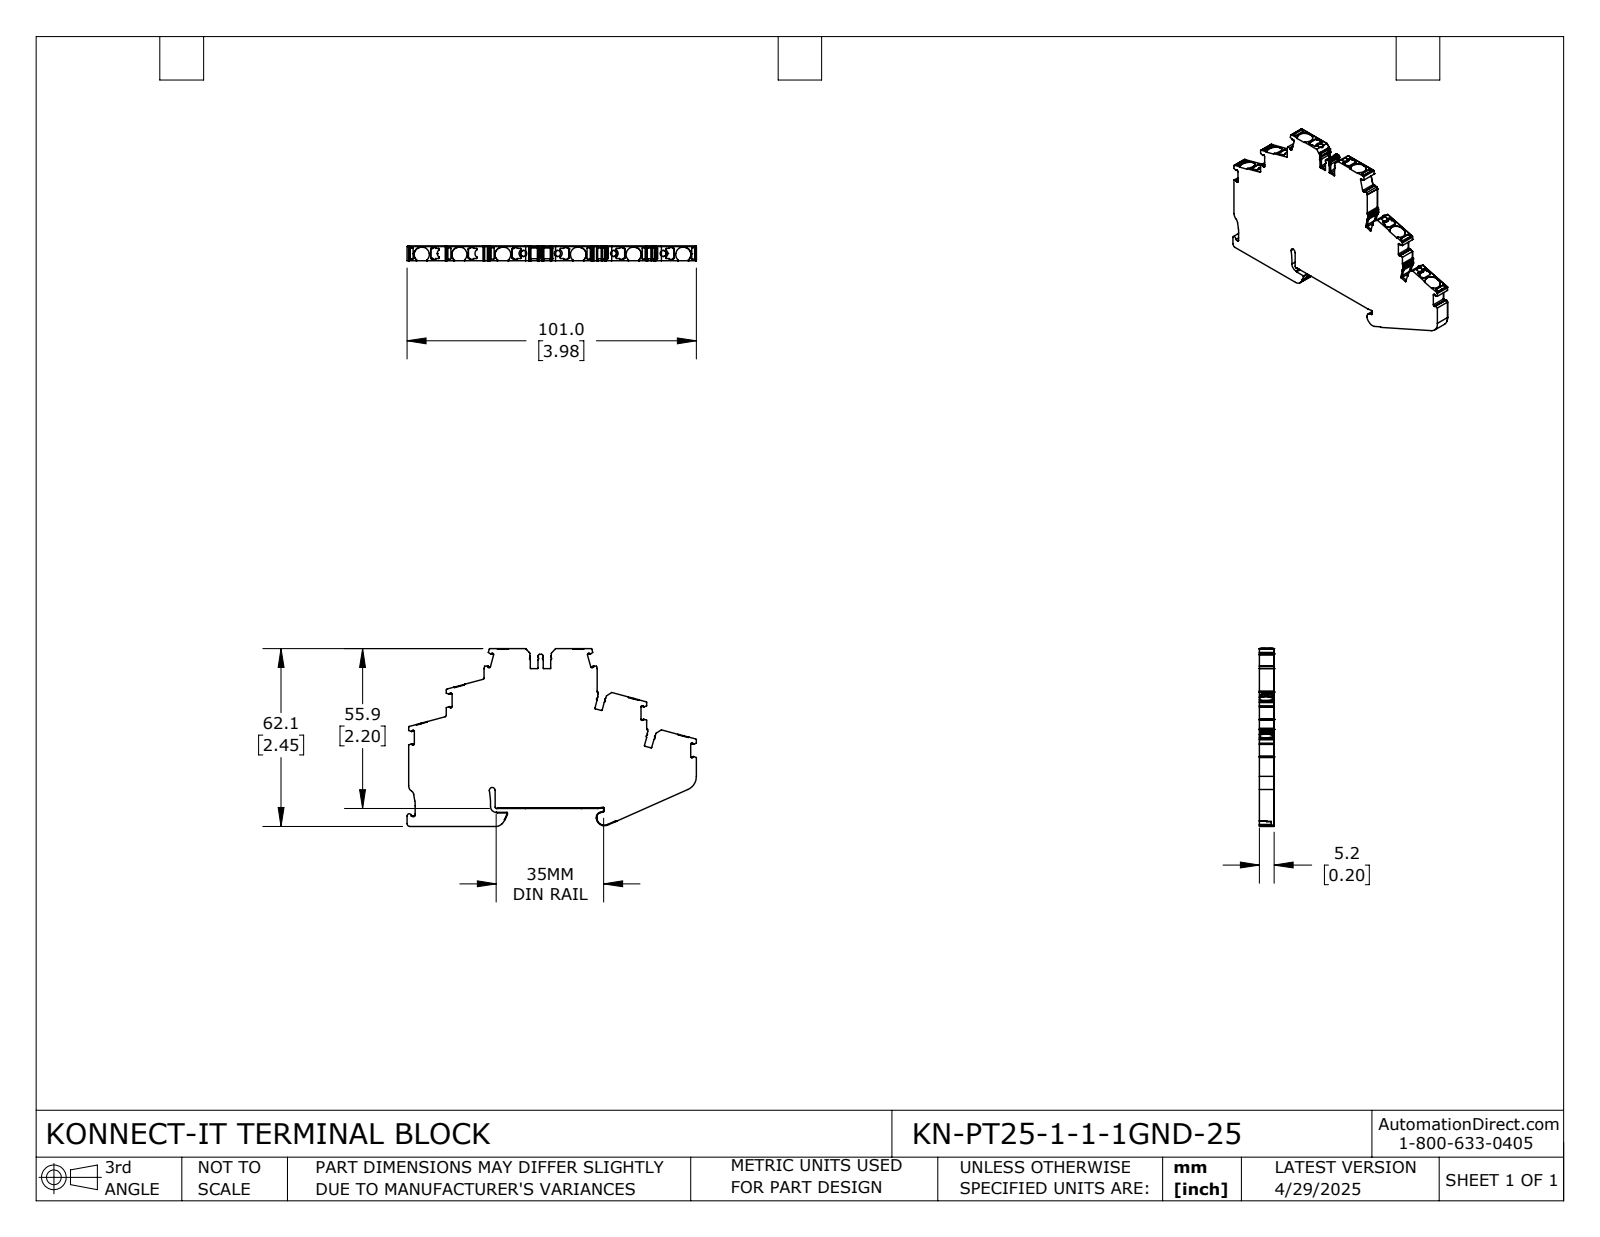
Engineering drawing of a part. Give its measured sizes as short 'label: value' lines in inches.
name: KN-PT25-1-1-1GND-25
written by: SolidWorks 2024 (CONFIG_CONTROL_DESIGN)
unit: in
bodies: 1 solid, 1010 faces (514 planar, 483 cylindrical, 13 other)
size: 3.977 × 2.445 × 0.203
volume: 1.35 in³; area: 16.8 in²
holes: 4× ⌀0.083
rounds: 119× R0.008, 47× R0.012, 37× R0.004, 24× R0.02, 23× R0.016, 14× R0.024, 12× R0.006, 12× R0.01
face distances: 0.203, 2.191, 0.246, 0.079, 2.437, 0.254, 2.183, 0.319, 0.682, 0.519
hole spacings: 0.466, 0.792
